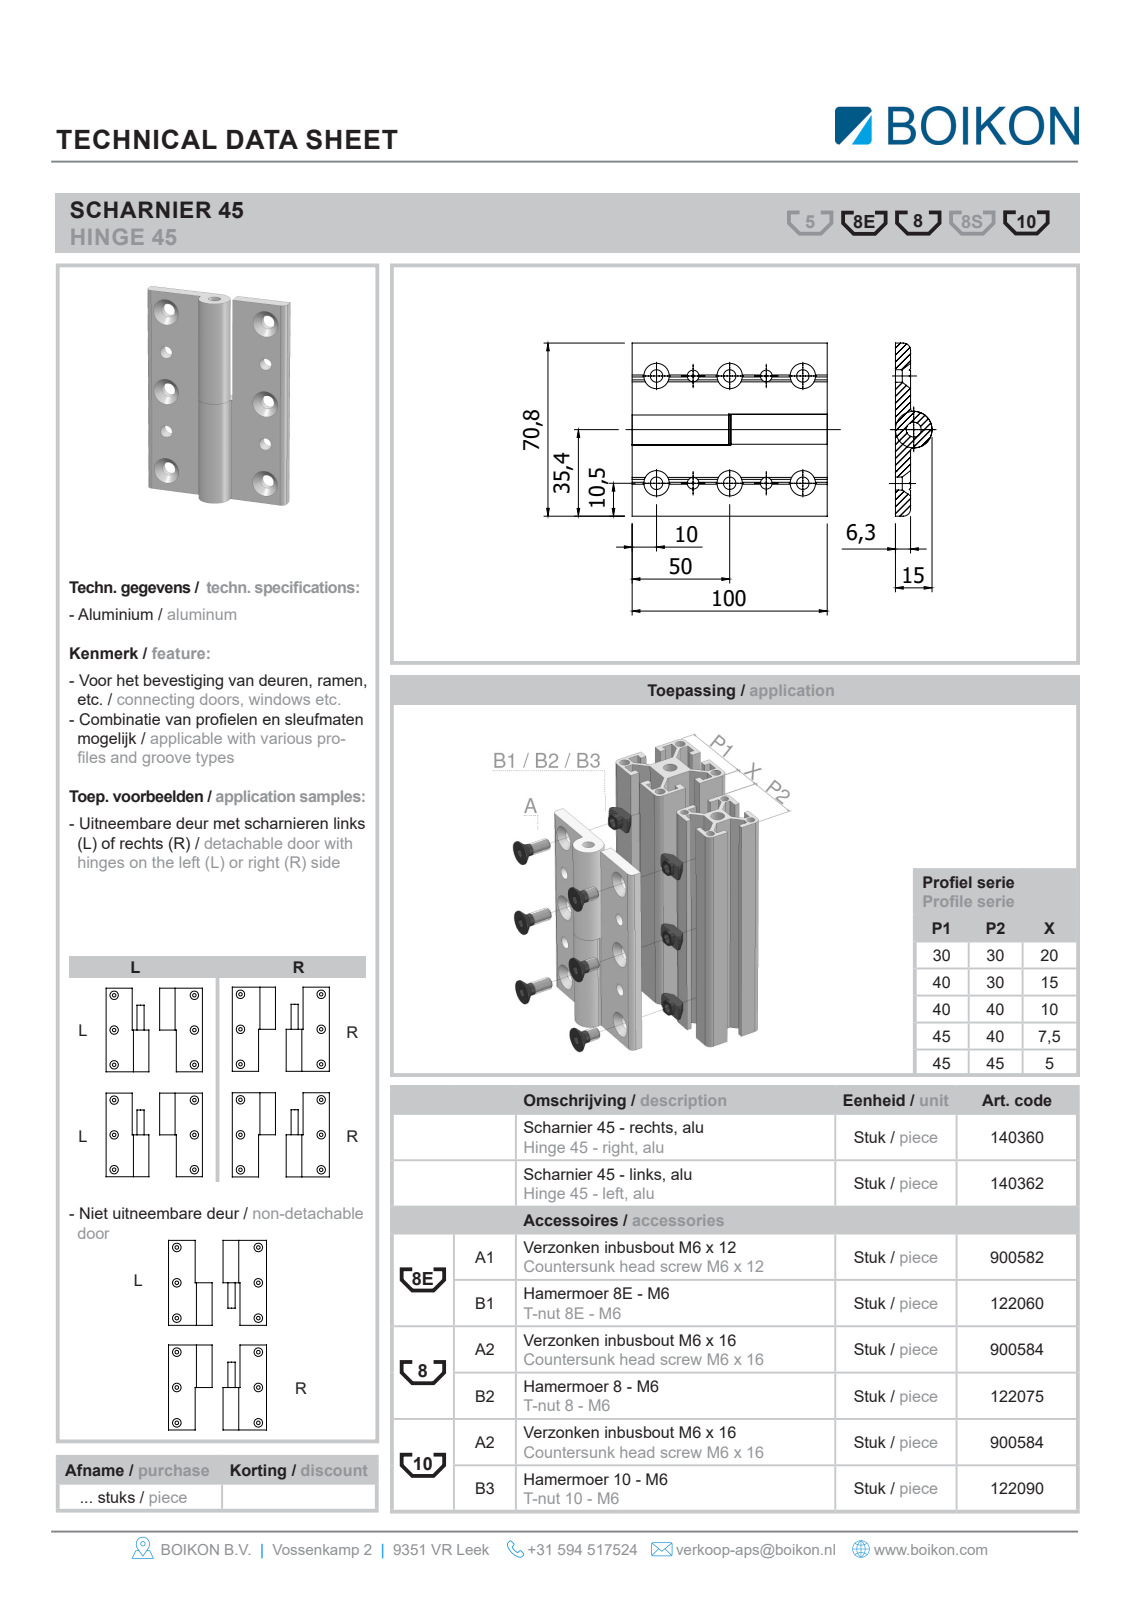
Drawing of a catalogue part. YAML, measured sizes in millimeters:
part_name: "Root; 140362Scharnier links 45 aluBOIKON; PEN"
step_written_by: "HiCAD 2013 1802.4 Build 509 (AUTOMOTIVE_DESIGN)"
units: millimeters
bodies: {solids: 3, faces: 43, planar: 18, cylindrical: 19, other: 6}
overall_size: [100, 70, 15]
volume: 47528
surface_area: 21770
round_holes:
  - {diameter: 6.6, count: 6}
  - {diameter: 6, count: 5}
round_bosses_or_shafts:
  - {diameter: 15, count: 1}
partial_cylinders:
  - {radius: 0.5, count: 2}
  - {radius: 2.5, count: 2}
face_to_face_distances: [6, 50, 26.5, 43.5, 100, 70, 17, 15, 27.5, 42.5]
hole_center_spacings: [20, 53.85, 40, 64.03, 50, 60, 78.1, 80]
